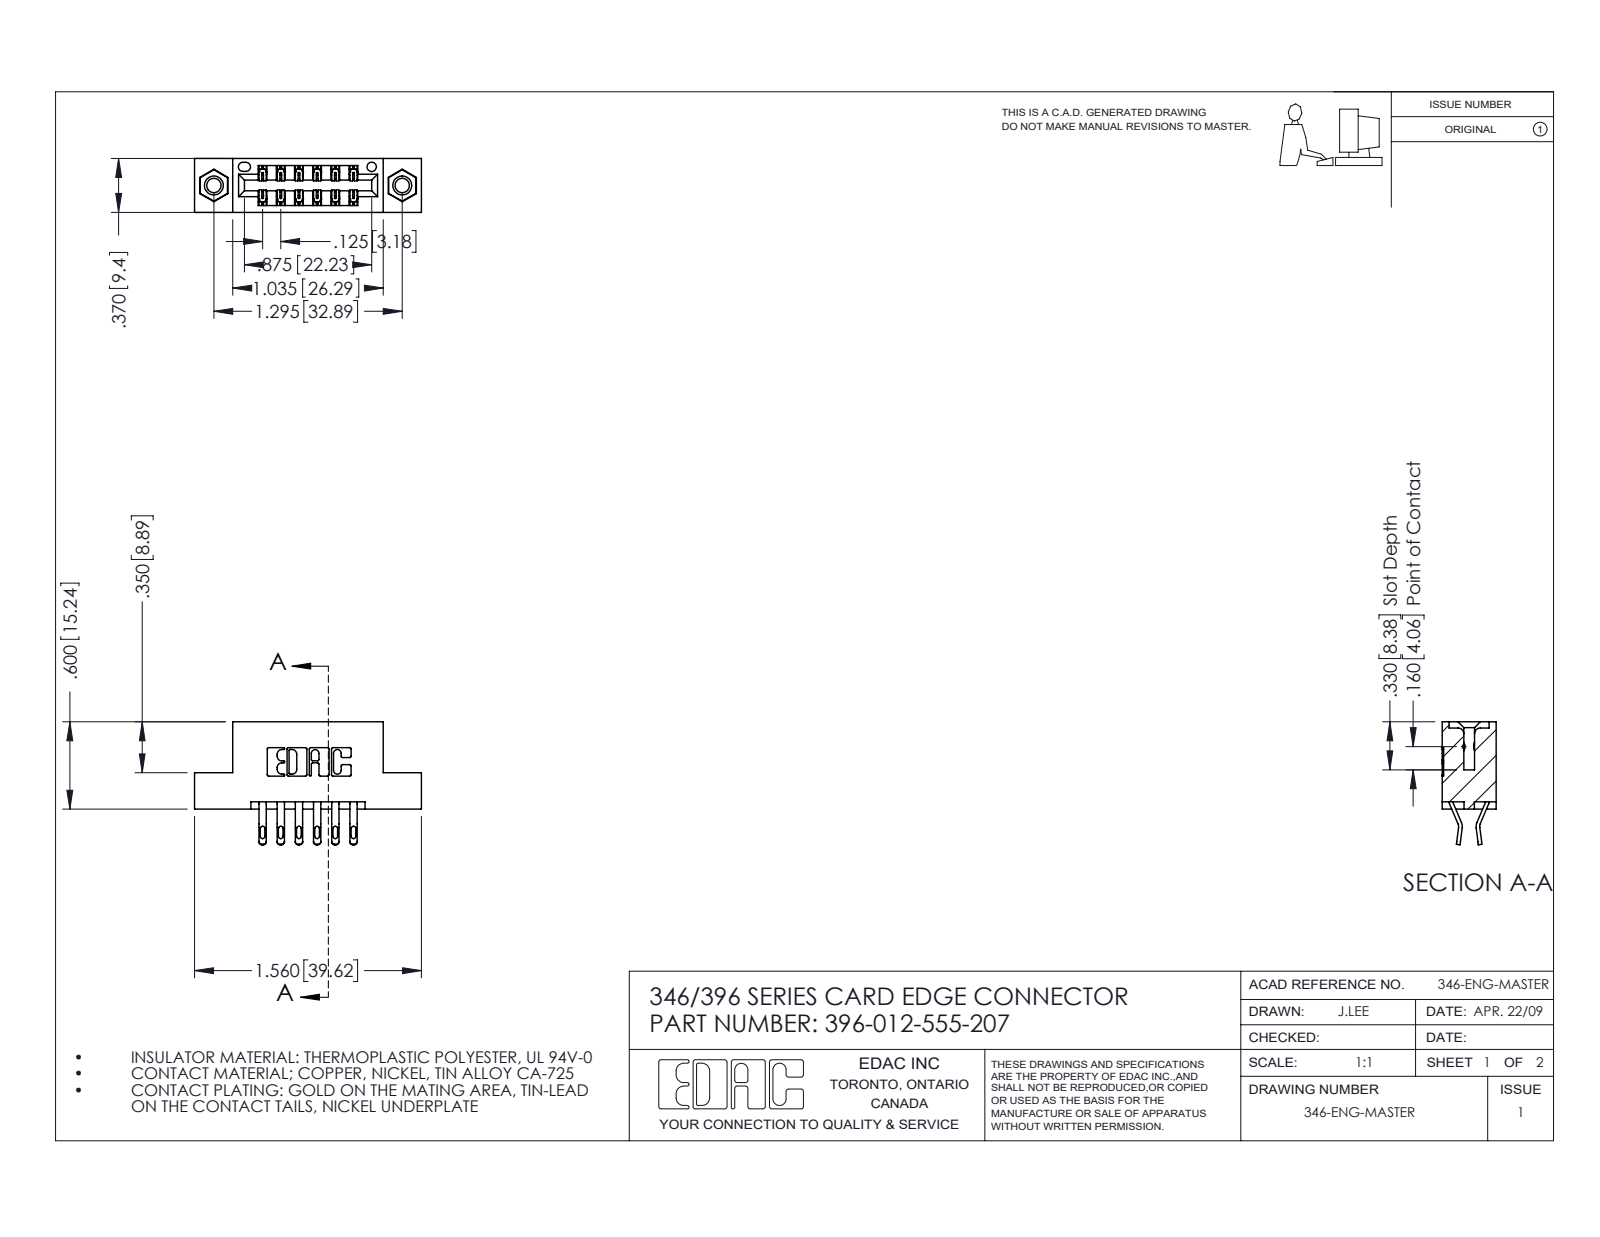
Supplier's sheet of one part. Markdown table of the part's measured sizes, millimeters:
| quantity | value |
| --- | --- |
| part name | 396-012-555-207; 346 Part_Flush Mounting Lugs - 0.156 Dia-TI; 345-250-001_345-250-005-103; 345-292-001_555 Tail |
| STEP written by | SolidWorks 2016 (CONFIG_CONTROL_DESIGN) |
| units | millimeters |
| bodies | 15 solids, 878 faces (504 planar, 358 cylindrical, 16 other) |
| overall size | 39.6 × 21.5 × 9.4 |
| volume | 3 610 mm³ |
| surface area | 4 548 mm² |
| round holes (diameter × count) | 2.5 × 2, 3.2 × 2, 4 × 2, 1.6 × 1 |
| round bosses / shafts (diameter × count) | 3.9 × 2 |
| partial cylindrical surfaces (radius × count) | 0.4 × 24, 0.5 × 24, 0.3 × 22, 0.2 × 18, 0.2 × 6, 0.8 × 6, 0.7 × 3, 0.3 × 2 |
| main face-to-face distances | 6.4, 9.4, 1.2, 8.2, 3.2, 3.8, 5.6, 2.5, 4.4, 0.6 |
| hole center spacings | 6.2, 27.7, 32.9 |
